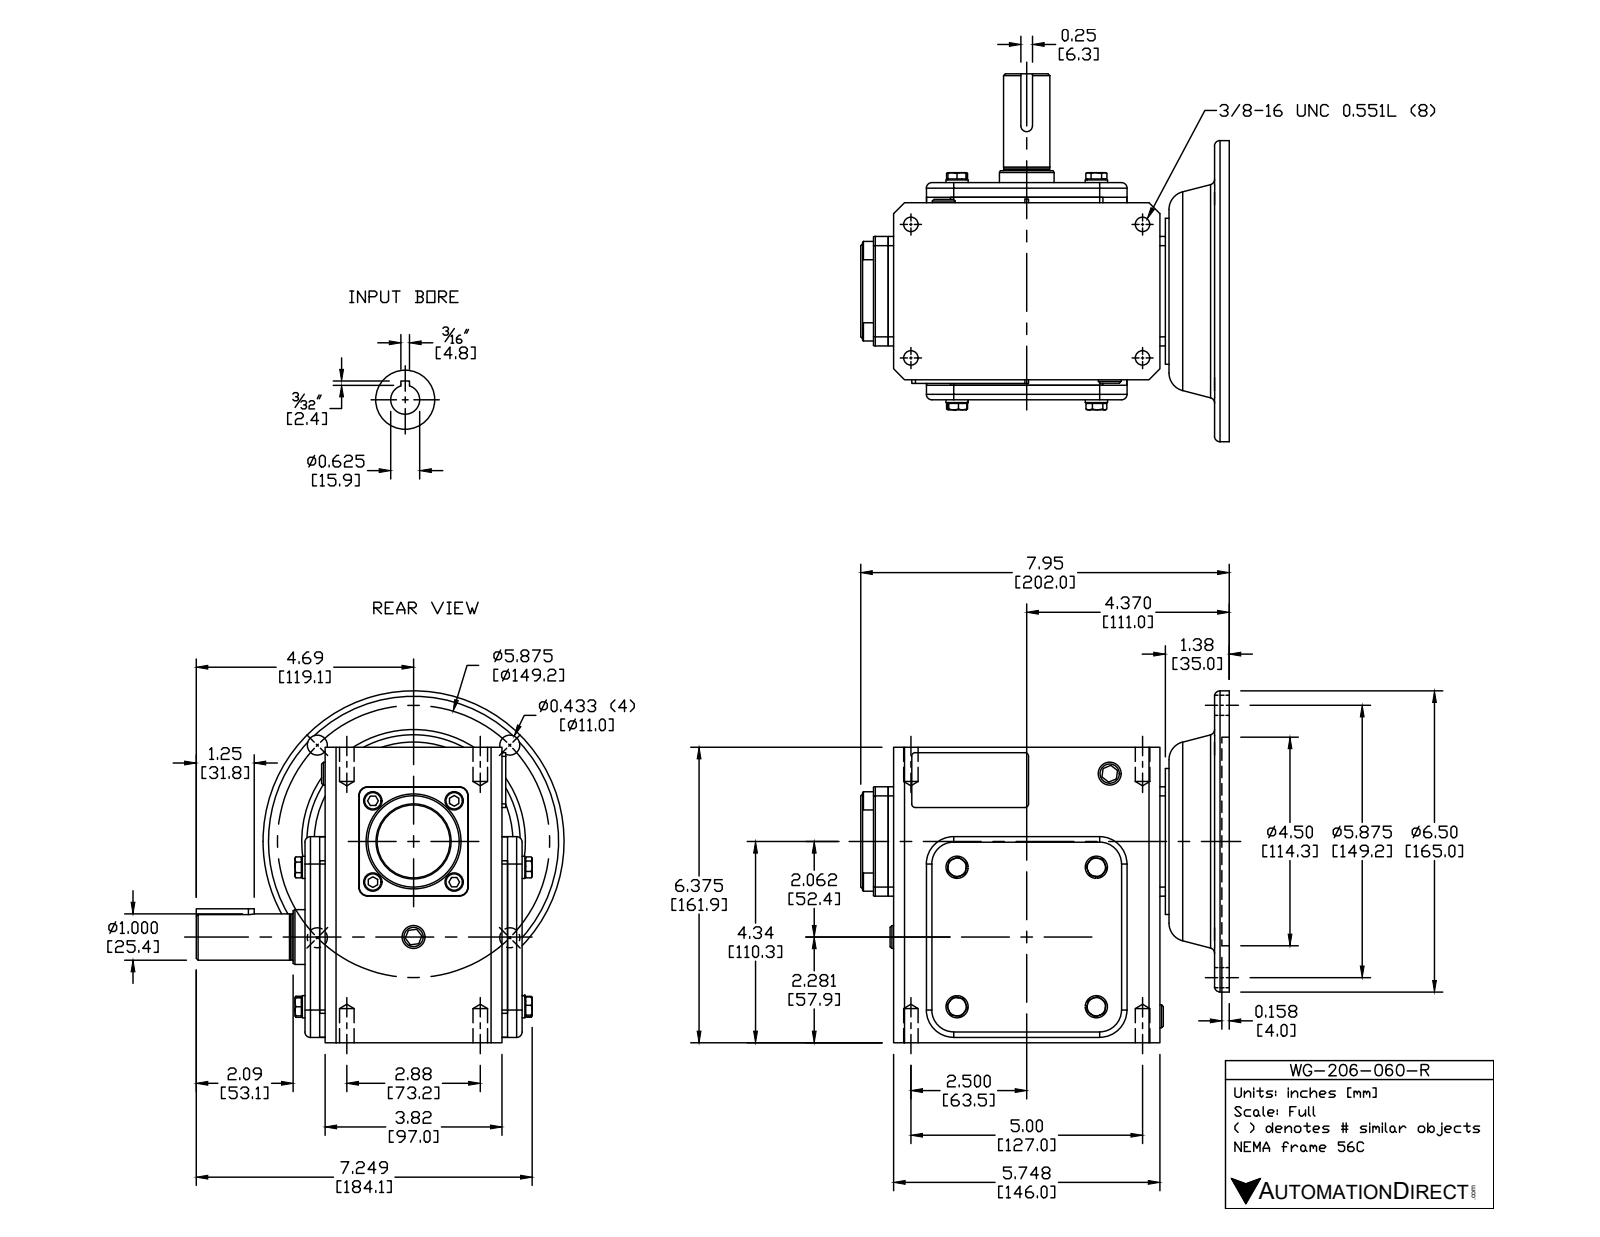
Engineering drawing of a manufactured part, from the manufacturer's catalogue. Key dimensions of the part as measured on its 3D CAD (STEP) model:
Part name (STEP PRODUCT): WG-206-060-R
STEP written by: SolidWorks 2015 (CONFIG_CONTROL_DESIGN)
Units: inches
Bodies: 43 solids, 610 faces (300 planar, 182 cylindrical, 128 other)
Overall size (bounding box): 7.953 × 7.938 × 7.591
Volume: 171.8 in³ · Surface area: 407.7 in²
Round holes (diameter × count): ⌀0.313 ×4, ⌀0.406 ×4, ⌀0.591 ×1, ⌀0.625 ×1, ⌀1.181 ×1, ⌀1.457 ×1, ⌀1.654 ×1, ⌀3.543 ×1, ⌀4.5 ×1
Round bosses / shafts (diameter × count): ⌀0.394 ×8, ⌀0.48 ×4, ⌀6.496 ×1, ⌀3.15 ×1, ⌀2.047 ×1, ⌀1.575 ×1, ⌀1.181 ×1, ⌀1.142 ×1
Partial cylindrical surfaces — rounded edges, fillets, slot ends (radius × count): R0.079 ×8, R0.118 ×8, R0.197 ×4, R0.591 ×4, R0.02 ×2, R0.039 ×2, R0.125 ×1, R2.717 ×1
Main face-to-face distances: 0.315, 0.118, 4.055, 4.37, 0.433, 4.252, 3.937, 6.375, 4.685, 0.709
Hole centre spacings: 2.937, 4.154, 2.077, 2.88, 4.631, 5, 5.77, 5.875
